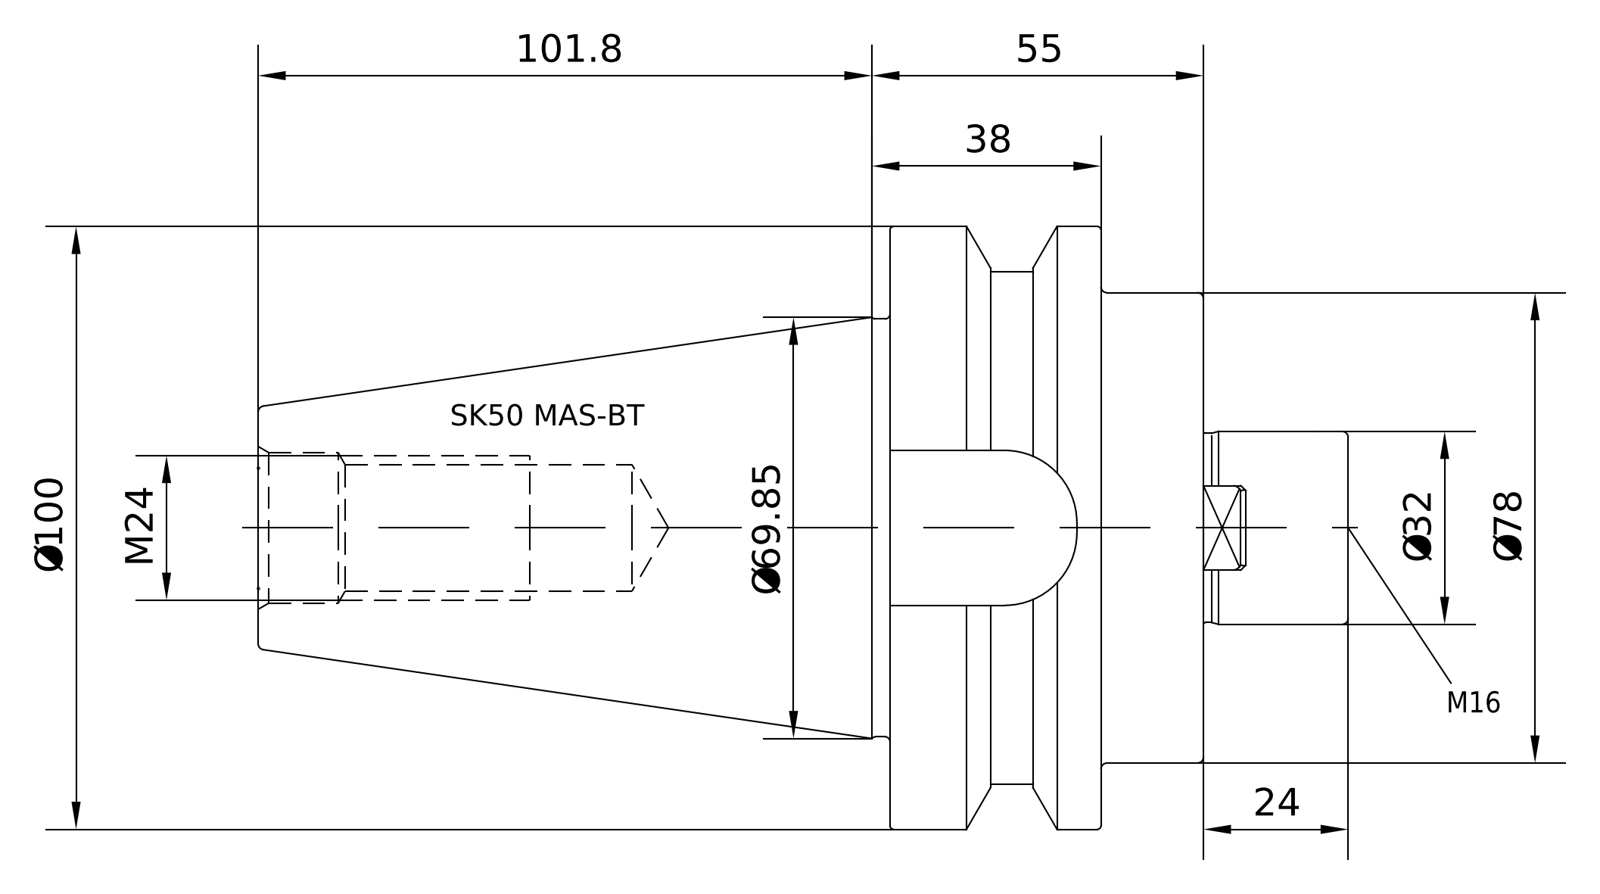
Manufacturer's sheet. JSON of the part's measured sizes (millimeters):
{"part_name": "50-550-32", "step_written_by": "PRO/ENGINEER BY PARAMETRIC TECHNOLOGY CORPORATION, 2010430 (CONFIG_CONTROL_DESIGN)", "units": "millimeters", "bodies": {"solids": 1, "faces": 113, "planar": 37, "cylindrical": 26, "other": 50}, "overall_size": [180.8, 99.97, 99.97], "volume_mm3": 564931, "surface_area_mm2": 62296, "round_holes": [[14, 1], [16, 1], [20.75, 1], [25.02, 1], [25.7, 1]], "round_bosses_or_shafts": [[99.97, 1], [84.75, 1], [78, 1], [69.15, 1], [32, 1], [24.01, 1]], "partial_cylinders_radius": [[12.9, 1]], "face_to_face_distances": [17, 52, 35, 24, 70.4, 76, 41, 104.8, 139.8, 156.8]}
